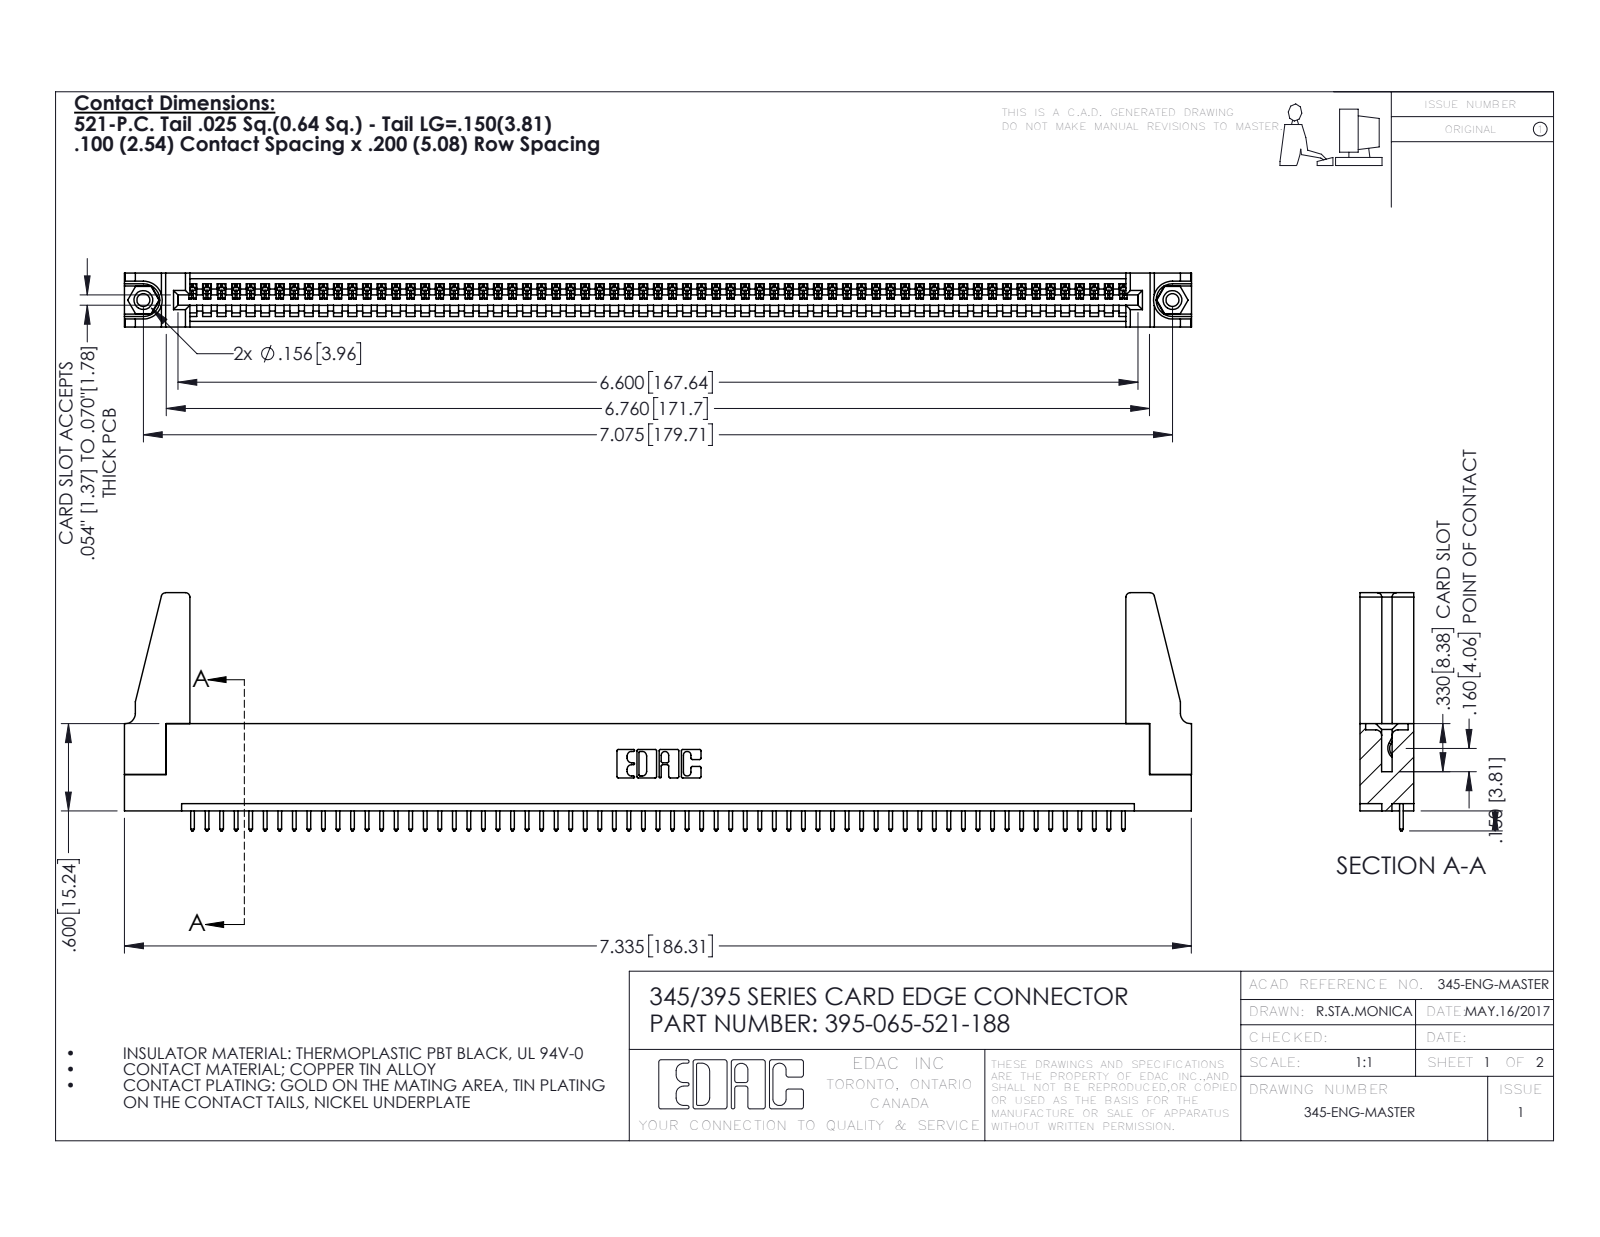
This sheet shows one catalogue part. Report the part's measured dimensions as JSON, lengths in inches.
{"part_name": "395-065-521-188; 345-292-001_345-293-121; 345-250-001_345-250-001-102; 345 Part_Flush Mounting Lugs - 0.156 Dia-TH (+1 more)", "step_written_by": "SolidWorks 2016 (CONFIG_CONTROL_DESIGN)", "units": "inches", "bodies": {"solids": 70, "faces": 4020, "planar": 2752, "cylindrical": 1252, "other": 16}, "overall_size": [7.336, 1.637, 0.37], "volume_in3": 1.279, "surface_area_in2": 40.68, "round_holes": [[0.089, 2], [0.125, 2], [0.156, 2], [0.064, 1]], "round_bosses_or_shafts": [[0.155, 2]], "partial_cylinders_radius": [[0.006, 130], [0.01, 130], [0.01, 22], [0.03, 8], [0.007, 6], [0.031, 6], [0.026, 3], [0.031, 2]], "face_to_face_distances": [0.072, 0.298, 0.37, 0.2, 0.098, 0.272, 0.025, 0.225, 0.149, 0.072], "hole_center_spacings": [0.27, 6.839, 7.075]}
